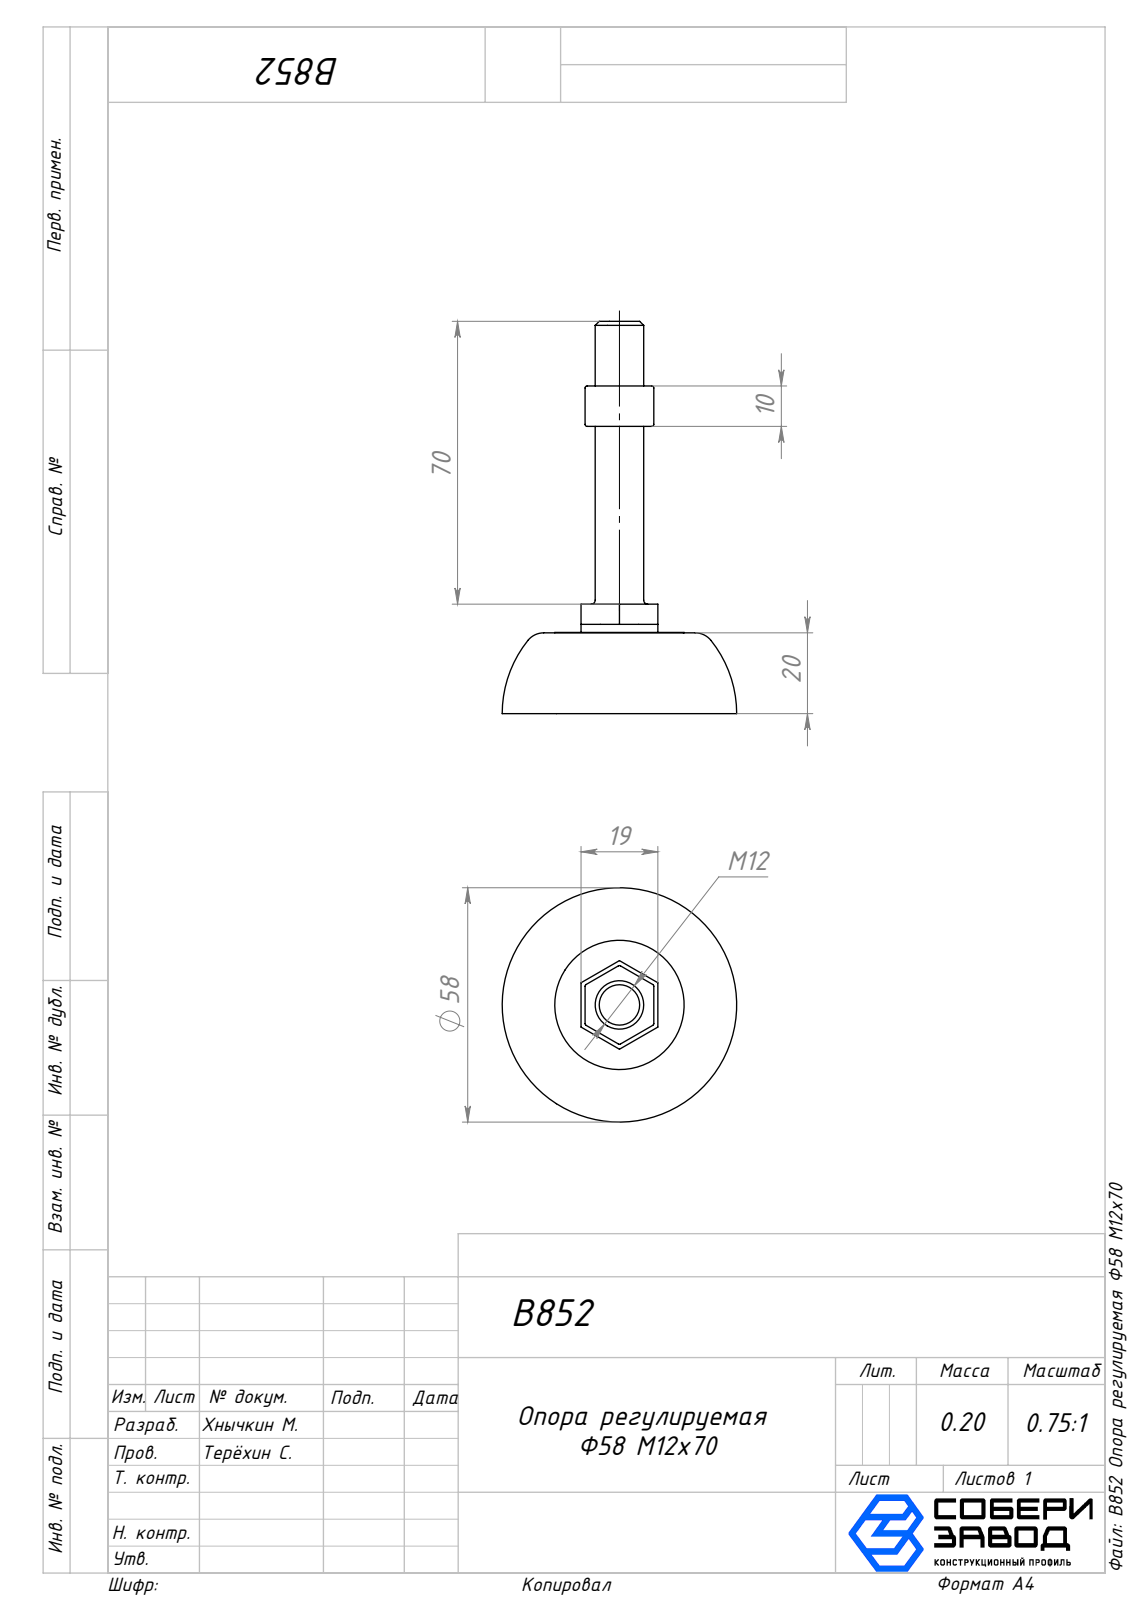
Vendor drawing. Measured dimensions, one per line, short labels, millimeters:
name: Опора_00; Гайка_00; Вал_00; Мал. гайка_00 (+1 more)
written by: SolidWorks 2025 (AUTOMOTIVE_DESIGN)
unit: mm
bodies: 4 solids, 128 faces (36 planar, 50 cylindrical, 42 other)
size: 97.1 × 58 × 58
volume: 26 106 mm³; area: 14 808 mm²
holes: 1× ⌀4, 1× ⌀5, 1× ⌀8
bosses: 1× ⌀32, 1× ⌀19, 1× ⌀12
rounds: 36× R0.5
face distances: 19.9, 20.1, 1, 18, 20, 17, 10, 19, 27.1, 7.2
